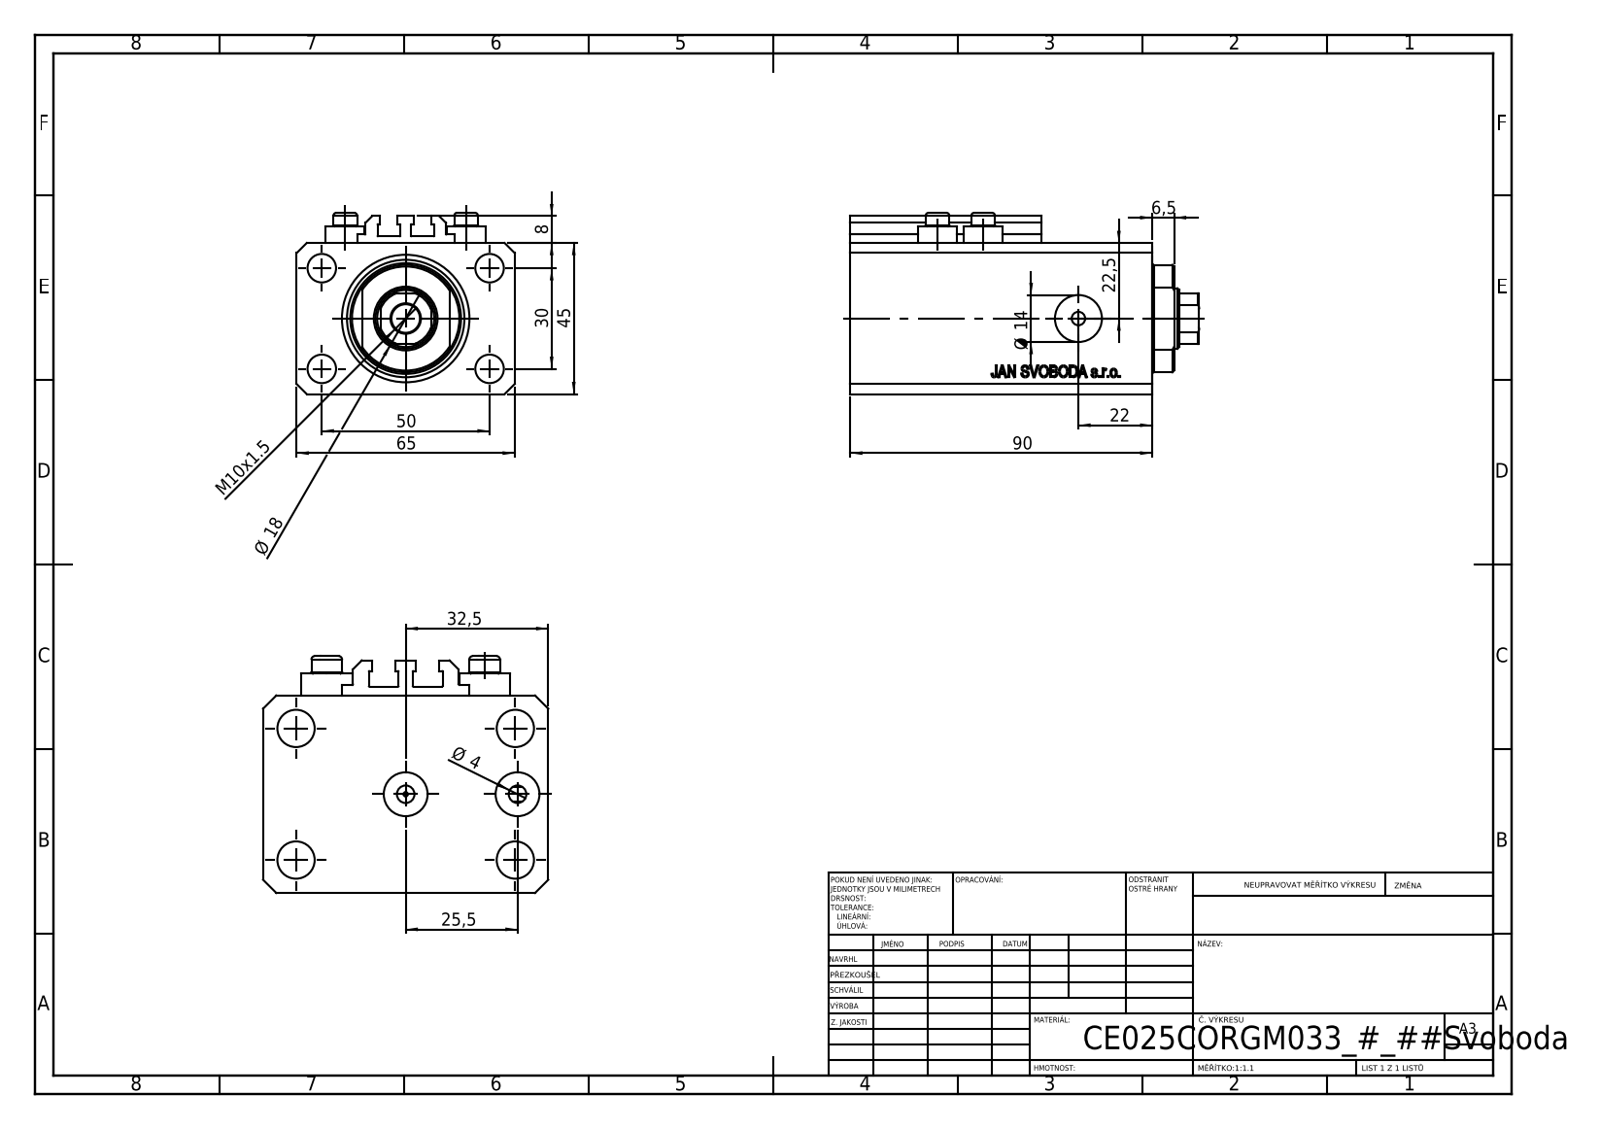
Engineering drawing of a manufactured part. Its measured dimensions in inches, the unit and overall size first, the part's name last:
Units: inches
Overall size (bounding box): 4.094 × 2.559 × 2.126
Round holes (diameter × count): ⌀0.157 ×8, ⌀0.335 ×5, ⌀0.394 ×2, ⌀0.551 ×2, ⌀0.049 ×1, ⌀0.709 ×1, ⌀0.984 ×1, ⌀1.496 ×1
Round bosses / shafts (diameter × count): ⌀0.457 ×4, ⌀0.276 ×4
Partial cylindrical surfaces — rounded edges, fillets, slot ends (radius × count): R0.008 ×10, R0.335 ×1, R0.63 ×1
Main face-to-face distances: 1.772, 2.559, 0.551, 3.543, 2.992, 1.85, 0.272, 2.72, 3.272, 0.118
Hole centre spacings: 1.148, 0.535, 0.591, 1.181, 1.417, 1.515, 1.969, 2.074
Volume: 14.94 in³ · Surface area: 100.7 in²
Bodies: 8 solids, 1039 faces (505 planar, 88 cylindrical, 446 other)
Part name (STEP PRODUCT): V250CE_VC_C; V250CE_C_VCP; V250CE_C_Body; ALLEN BOLT V250CE
STEP written by: SolidWorks 2019 (CONFIG_CONTROL_DESIGN)
